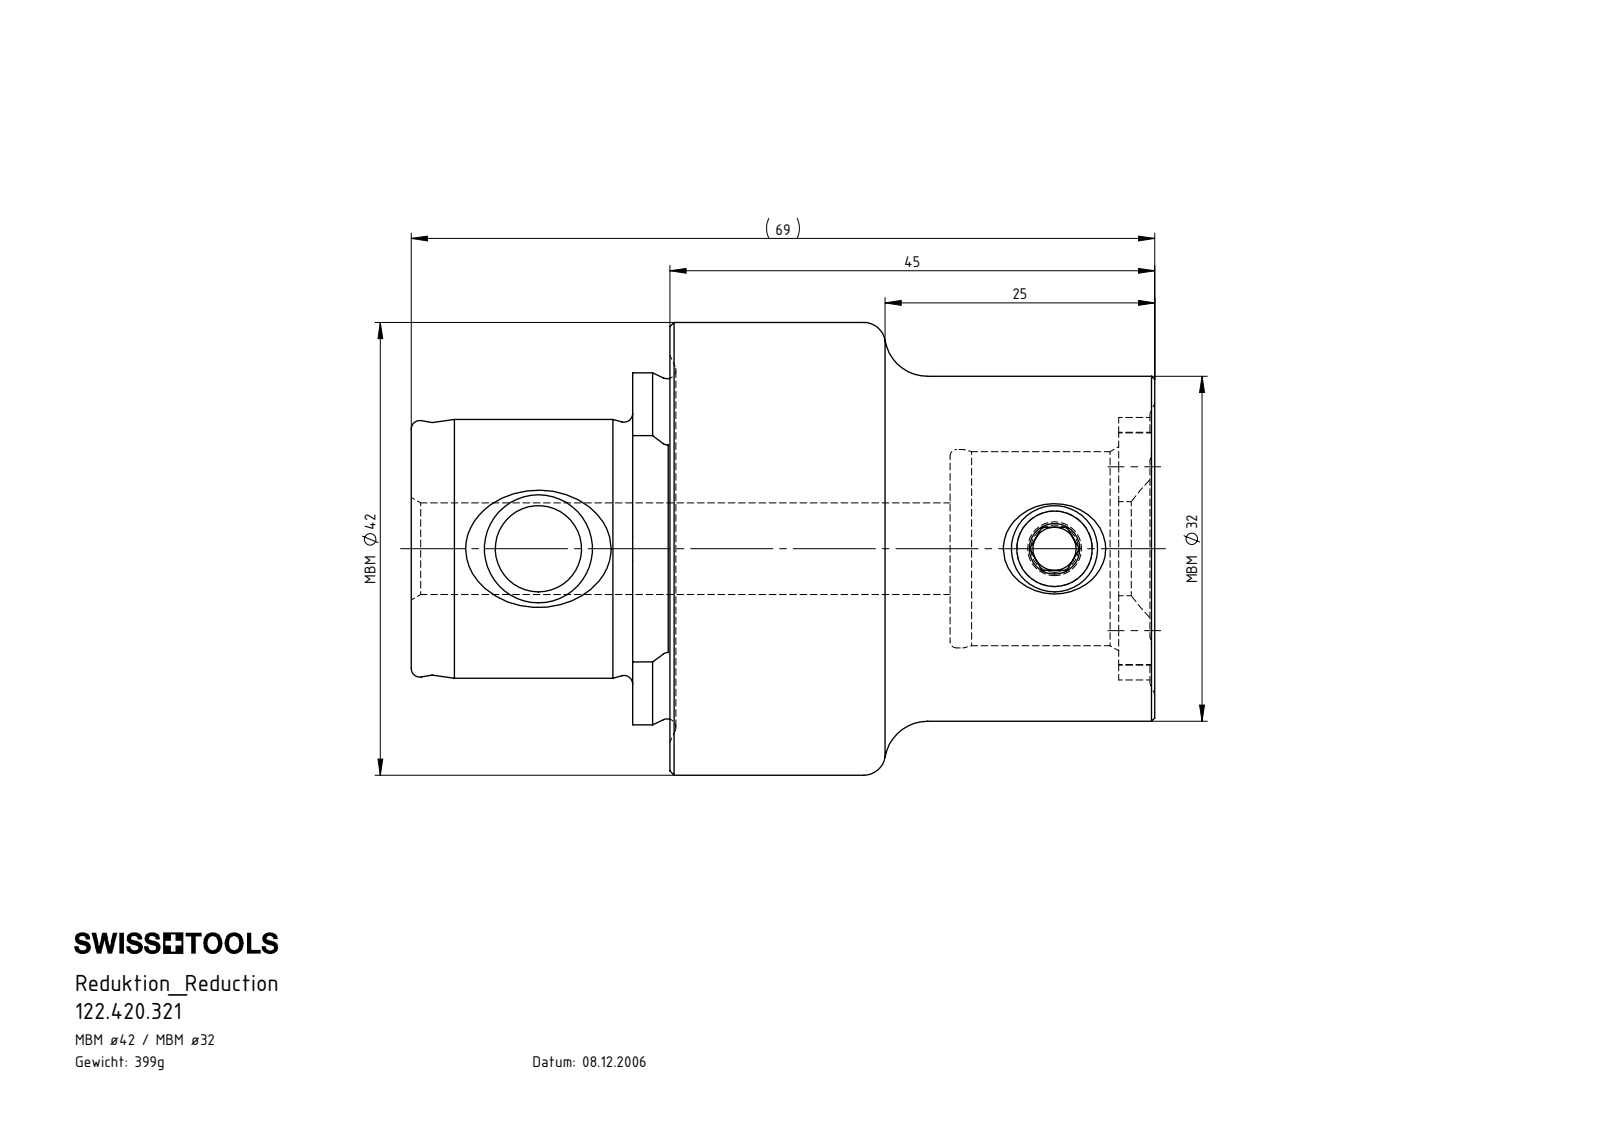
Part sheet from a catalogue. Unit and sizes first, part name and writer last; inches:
Units: inches
Overall size (bounding box): 2.717 × 1.654 × 1.654
Round holes (diameter × count): ⌀0.157 ×1, ⌀0.276 ×1, ⌀0.315 ×1, ⌀0.335 ×1, ⌀0.709 ×1, ⌀0.724 ×1
Round bosses / shafts (diameter × count): ⌀1.654 ×1, ⌀1.26 ×1, ⌀0.945 ×1, ⌀0.315 ×1
Partial cylindrical surfaces — rounded edges, fillets, slot ends (radius × count): R0.126 ×4, R0.413 ×1, R0.48 ×1, R0.643 ×1
Main face-to-face distances: 0.945, 0.809, 0.136, 2.717, 1.907, 1.772, 1.969, 1.159, 1.024, 0.748
Hole centre spacings: 1.886
Volume: 3.101 in³ · Surface area: 19.11 in²
Bodies: 2 solids, 136 faces (35 planar, 34 cylindrical, 67 other)
Part name (STEP PRODUCT): MB4-MB3.K01.045_C; MB3-ER1.001.011_A; 122.420.321
STEP written by: SolidWorks 2017 (CONFIG_CONTROL_DESIGN)
